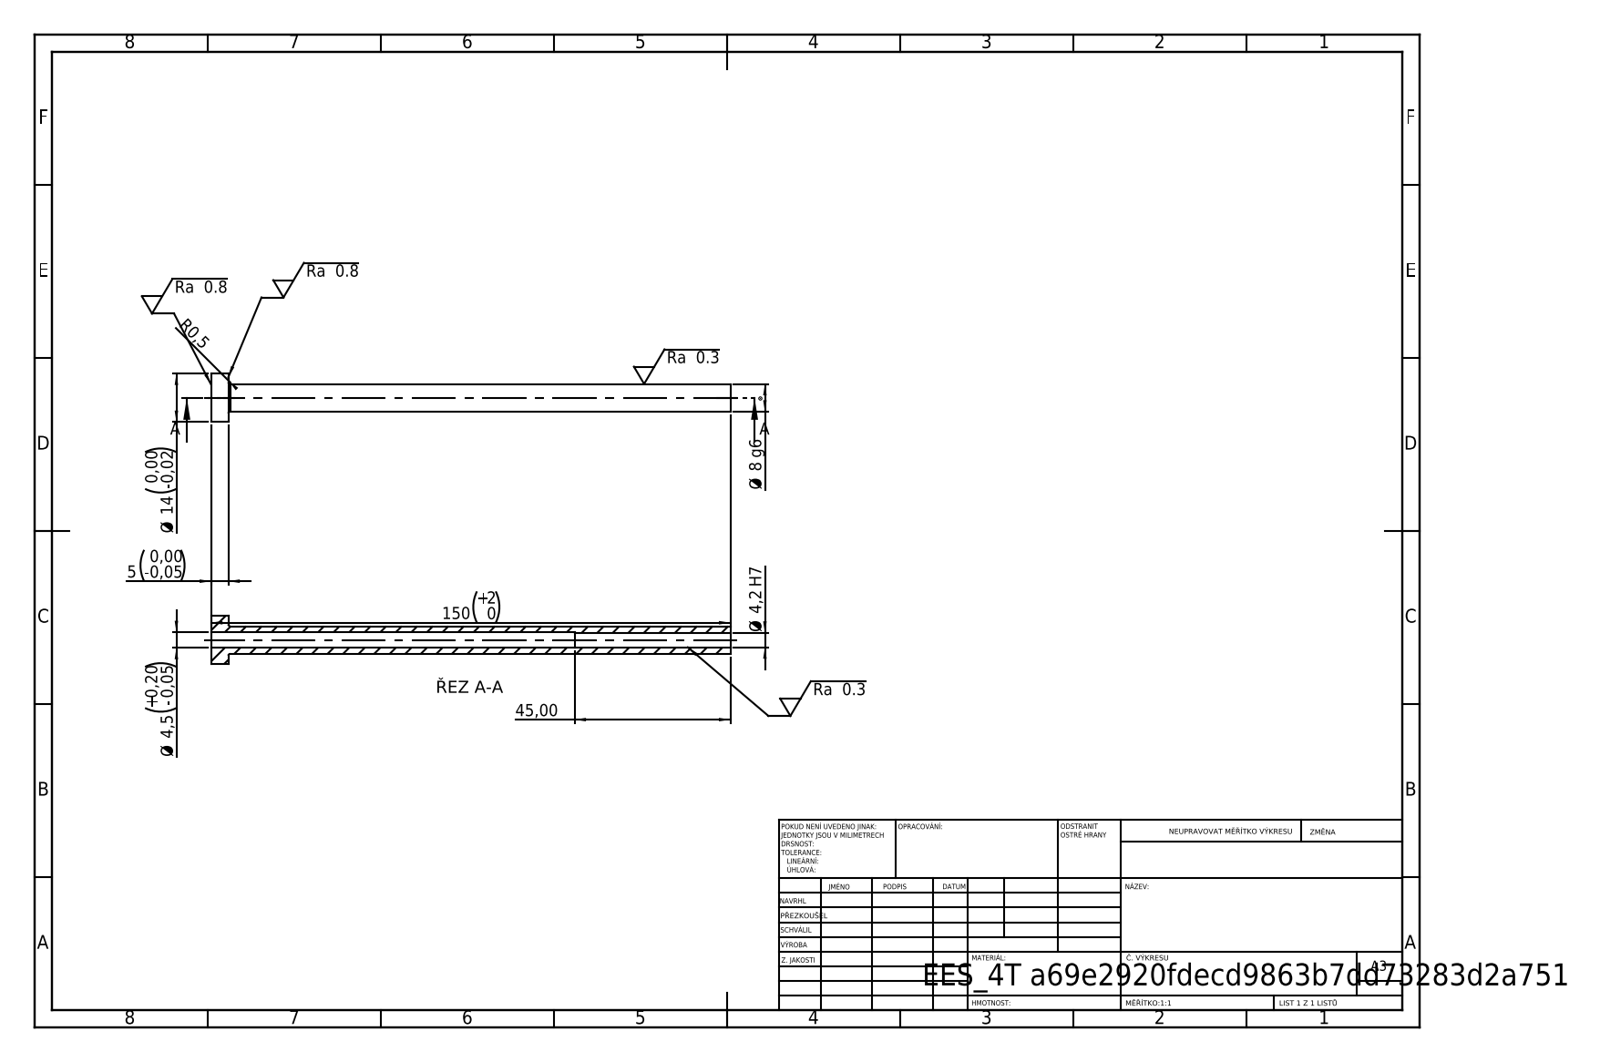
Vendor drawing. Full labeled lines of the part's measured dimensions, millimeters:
STEP written by: SolidWorks 2019 (CONFIG_CONTROL_DESIGN)
Units: millimetres
Bodies: 1 solid, 14 faces (4 planar, 8 cylindrical, 2 other)
Overall size (bounding box): 150 × 14 × 14
Volume: 5 766 mm³ · Surface area: 6 217 mm²
Round holes (diameter × count): ⌀4.2 ×1, ⌀4.5 ×1
Round bosses / shafts (diameter × count): ⌀14 ×1, ⌀8 ×1
Main face-to-face distances: 5, 150, 145, 105, 100, 45
